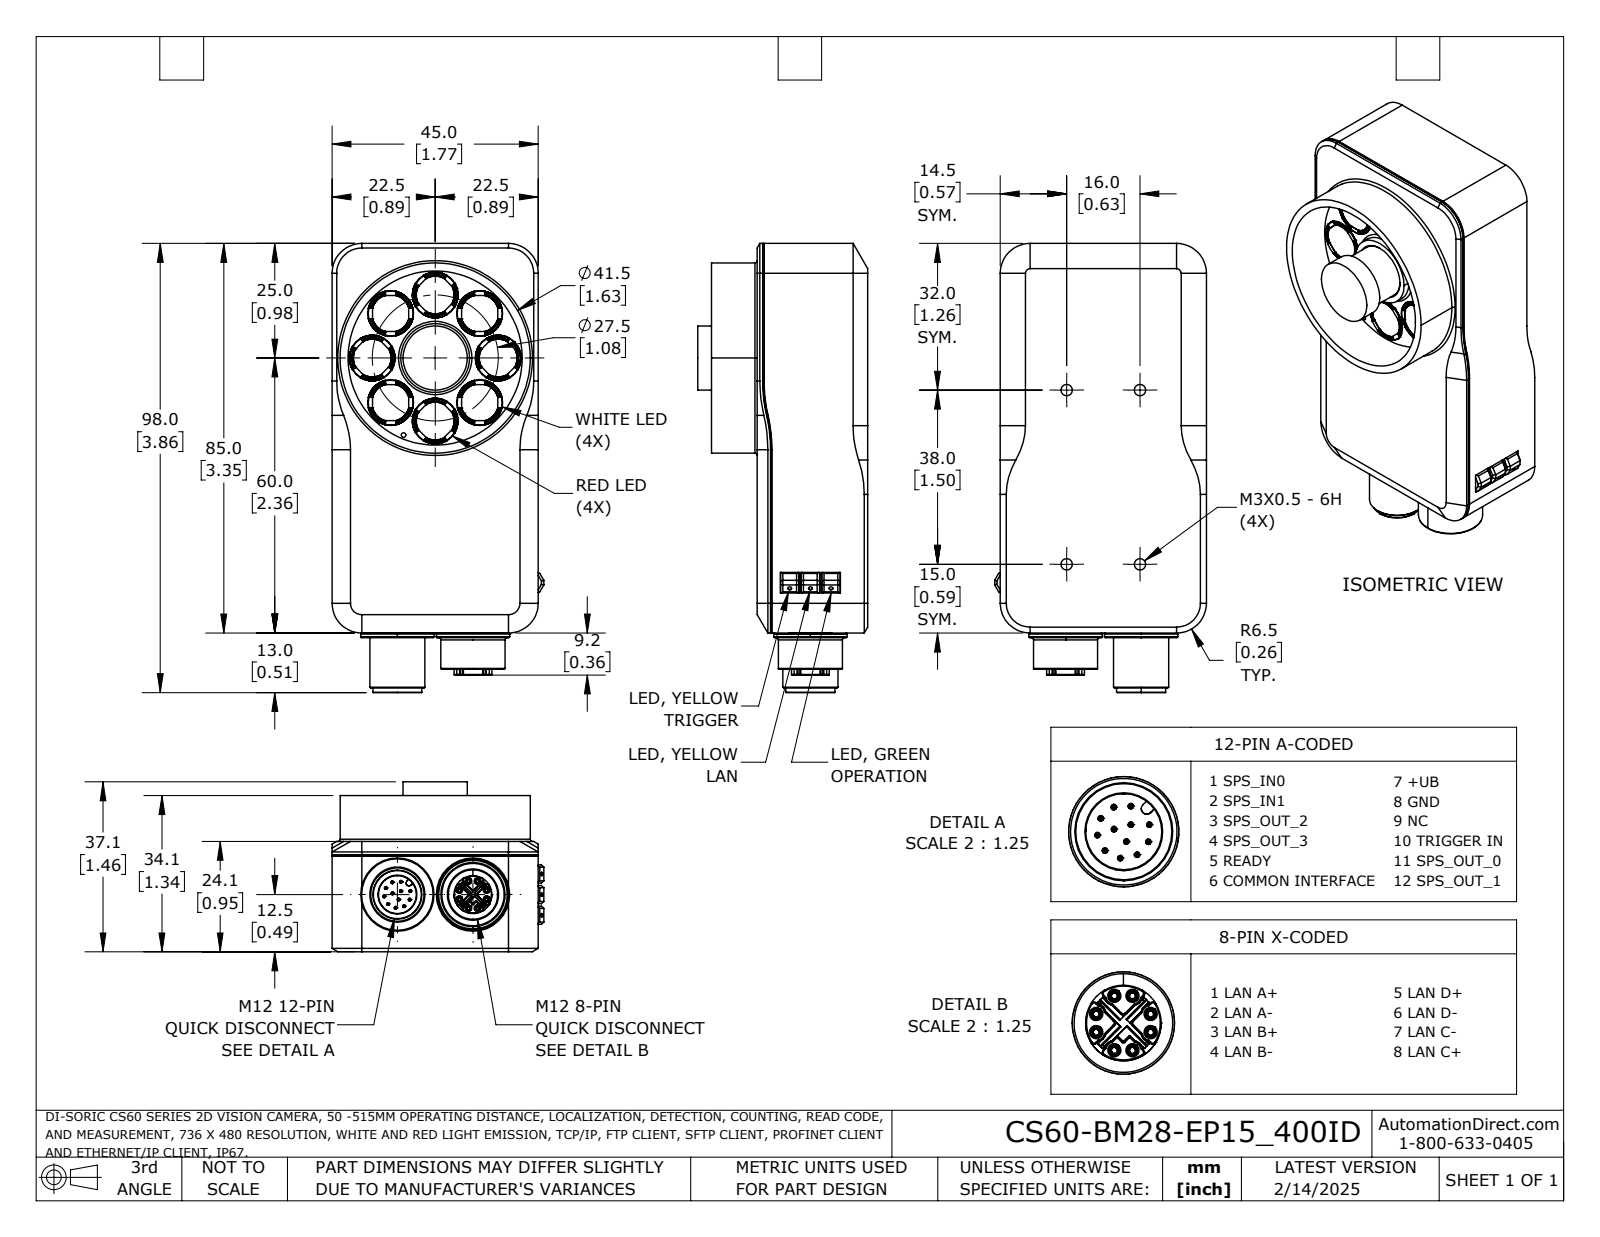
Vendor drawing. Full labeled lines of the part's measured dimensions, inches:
Part name (STEP PRODUCT): CS60-BM28-EP15_300
STEP written by: SolidWorks 2024 (AUTOMOTIVE_DESIGN)
Units: inches
Bodies: 1 solid, 2784 faces (1185 planar, 863 cylindrical, 736 other)
Overall size (bounding box): 3.858 × 1.819 × 1.461
Volume: 2.479 in³ · Surface area: 56.26 in²
Round holes (diameter × count): ⌀0.024 ×8, ⌀0.026 ×8, ⌀0.049 ×8, ⌀0.071 ×4, ⌀0.031 ×3, ⌀0.13 ×3, ⌀0.097 ×2, ⌀0.097 ×2, ⌀0.039 ×1, ⌀0.315 ×1, ⌀0.327 ×1, ⌀0.331 ×1
Round bosses / shafts (diameter × count): ⌀0.028 ×20, ⌀0.024 ×12, ⌀0.39 ×8, ⌀0.197 ×4, ⌀0.157 ×4, ⌀0.126 ×3, ⌀0.087 ×3, ⌀0.059 ×3
Partial cylindrical surfaces — rounded edges, fillets, slot ends (radius × count): R0.004 ×164, R0.008 ×48, R0.006 ×28, R0.02 ×19, R0.016 ×15, R0.012 ×12, R0.01 ×10, R0.045 ×10
Main face-to-face distances: 0.079, 0.118, 0.831, 1.693, 0.949, 0.87, 0.752, 1.772, 0.039, 1.614
Hole centre spacings: 0.123, 0.174, 0.078, 0.11, 0.177, 0.22, 0.234, 0.246
